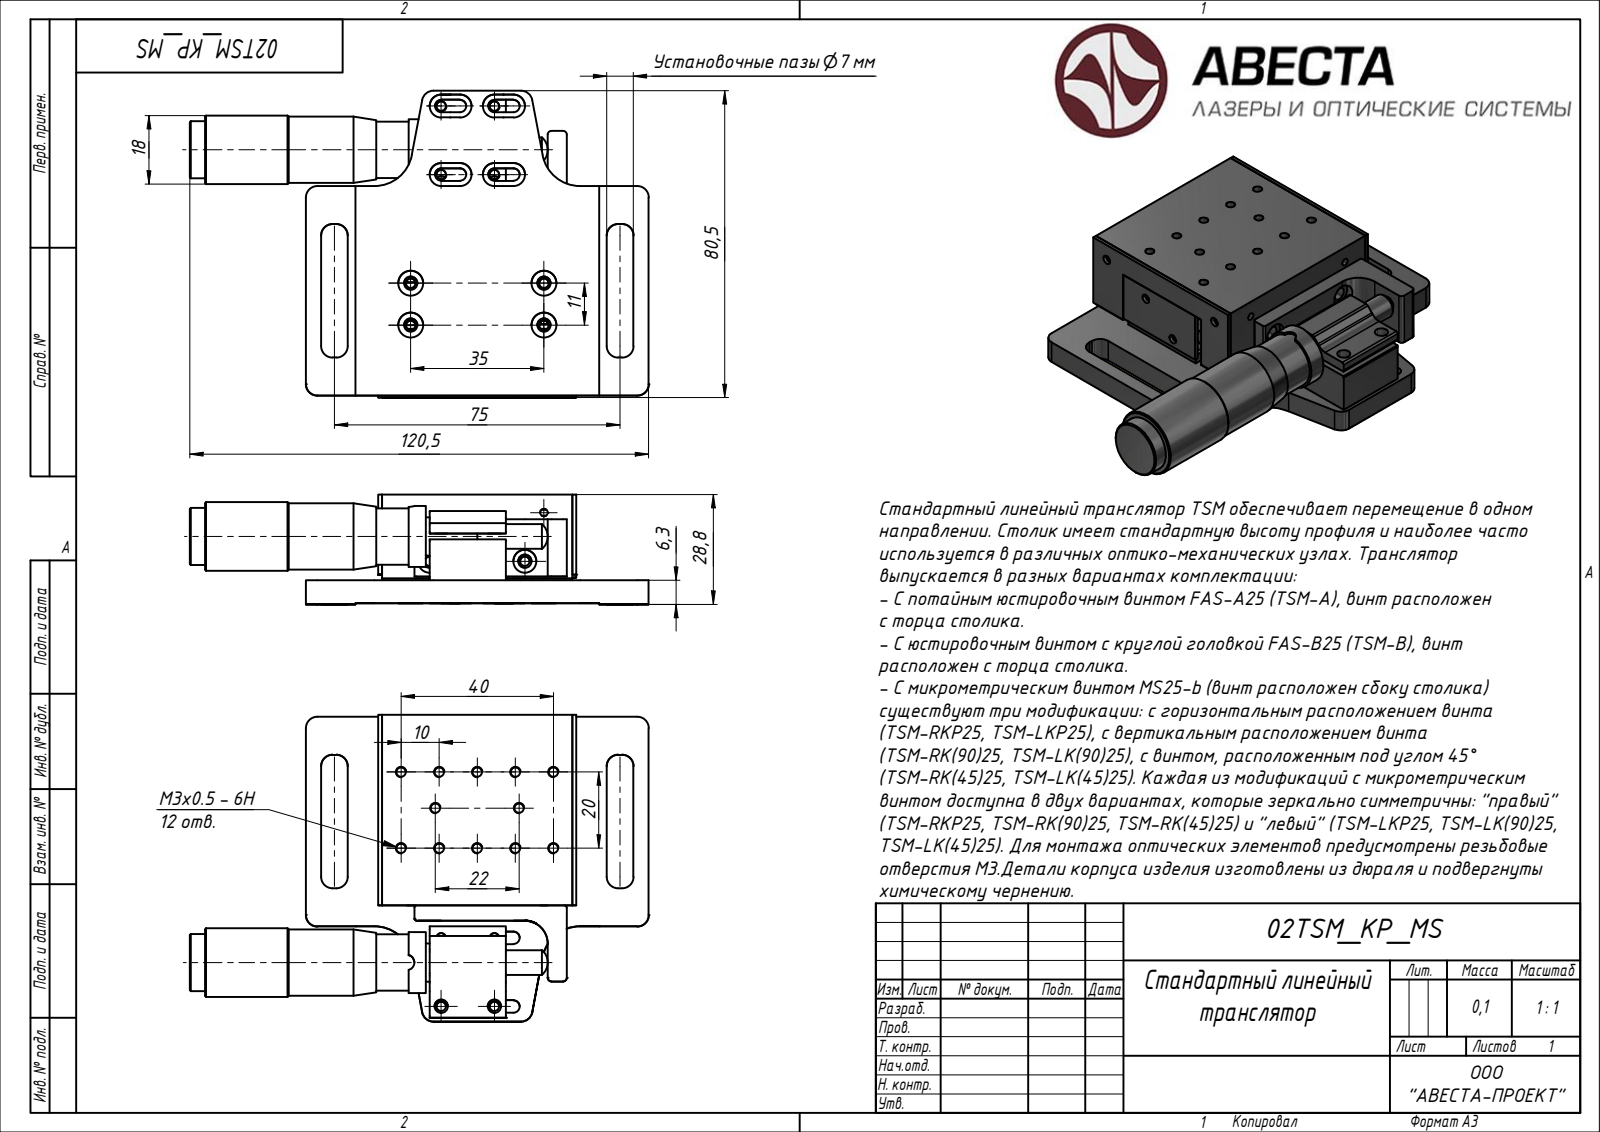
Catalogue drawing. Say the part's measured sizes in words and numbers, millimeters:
Its 3-D file was written by "ST-DEVELOPER v15 (AUTOMOTIVE_DESIGN)". It is 23 solids with 711 faces: 0 planar, 0 cylindrical and 711 other. Overall it measures 120.5 by 80.52 by 28.83 millimeters.
